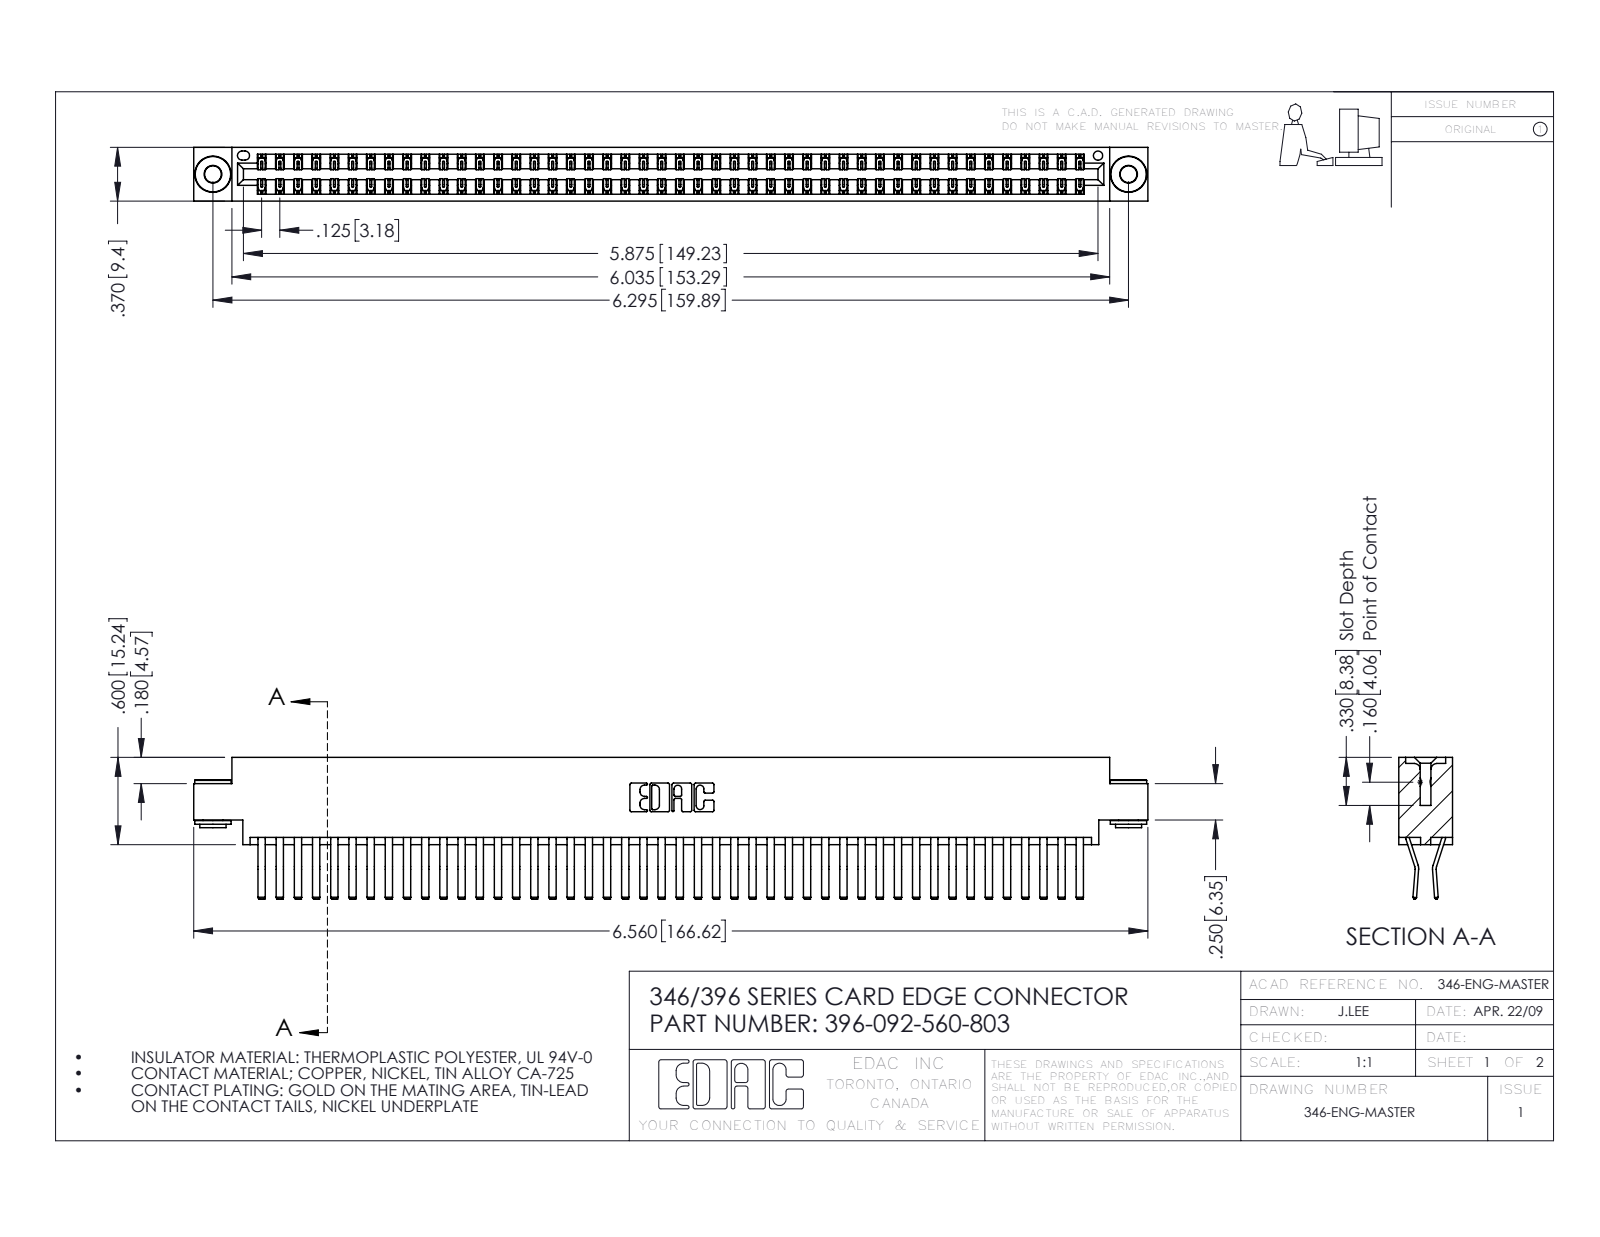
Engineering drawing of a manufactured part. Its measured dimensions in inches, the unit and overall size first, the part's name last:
Units: inches
Overall size (bounding box): 6.56 × 0.975 × 0.37
Round holes (diameter × count): ⌀0.116 ×2, ⌀0.156 ×2, ⌀0.064 ×1
Round bosses / shafts (diameter × count): ⌀0.25 ×2, ⌀0.18 ×2, ⌀0.136 ×2
Partial cylindrical surfaces — rounded edges, fillets, slot ends (radius × count): R0.006 ×138, R0.01 ×22, R0.007 ×6, R0.031 ×6, R0.026 ×3, R0.01 ×2, R0.014 ×2, R0.022 ×2
Main face-to-face distances: 0.048, 0.322, 0.37, 0.025, 0.25, 0.275, 0.072, 0.298, 0.148, 0.222
Hole centre spacings: 0.246, 6.086, 6.295
Volume: 1.022 in³ · Surface area: 38.88 in²
Bodies: 95 solids, 5132 faces (3310 planar, 1814 cylindrical, 8 other)
Part name (STEP PRODUCT): 346 Part_0.170 Offset - 0.156 Dia-TH; 396-092-560-803; 345-250-002_345-250-002-102; 345-292-001_560 Tail
STEP written by: SolidWorks 2016 (CONFIG_CONTROL_DESIGN)
